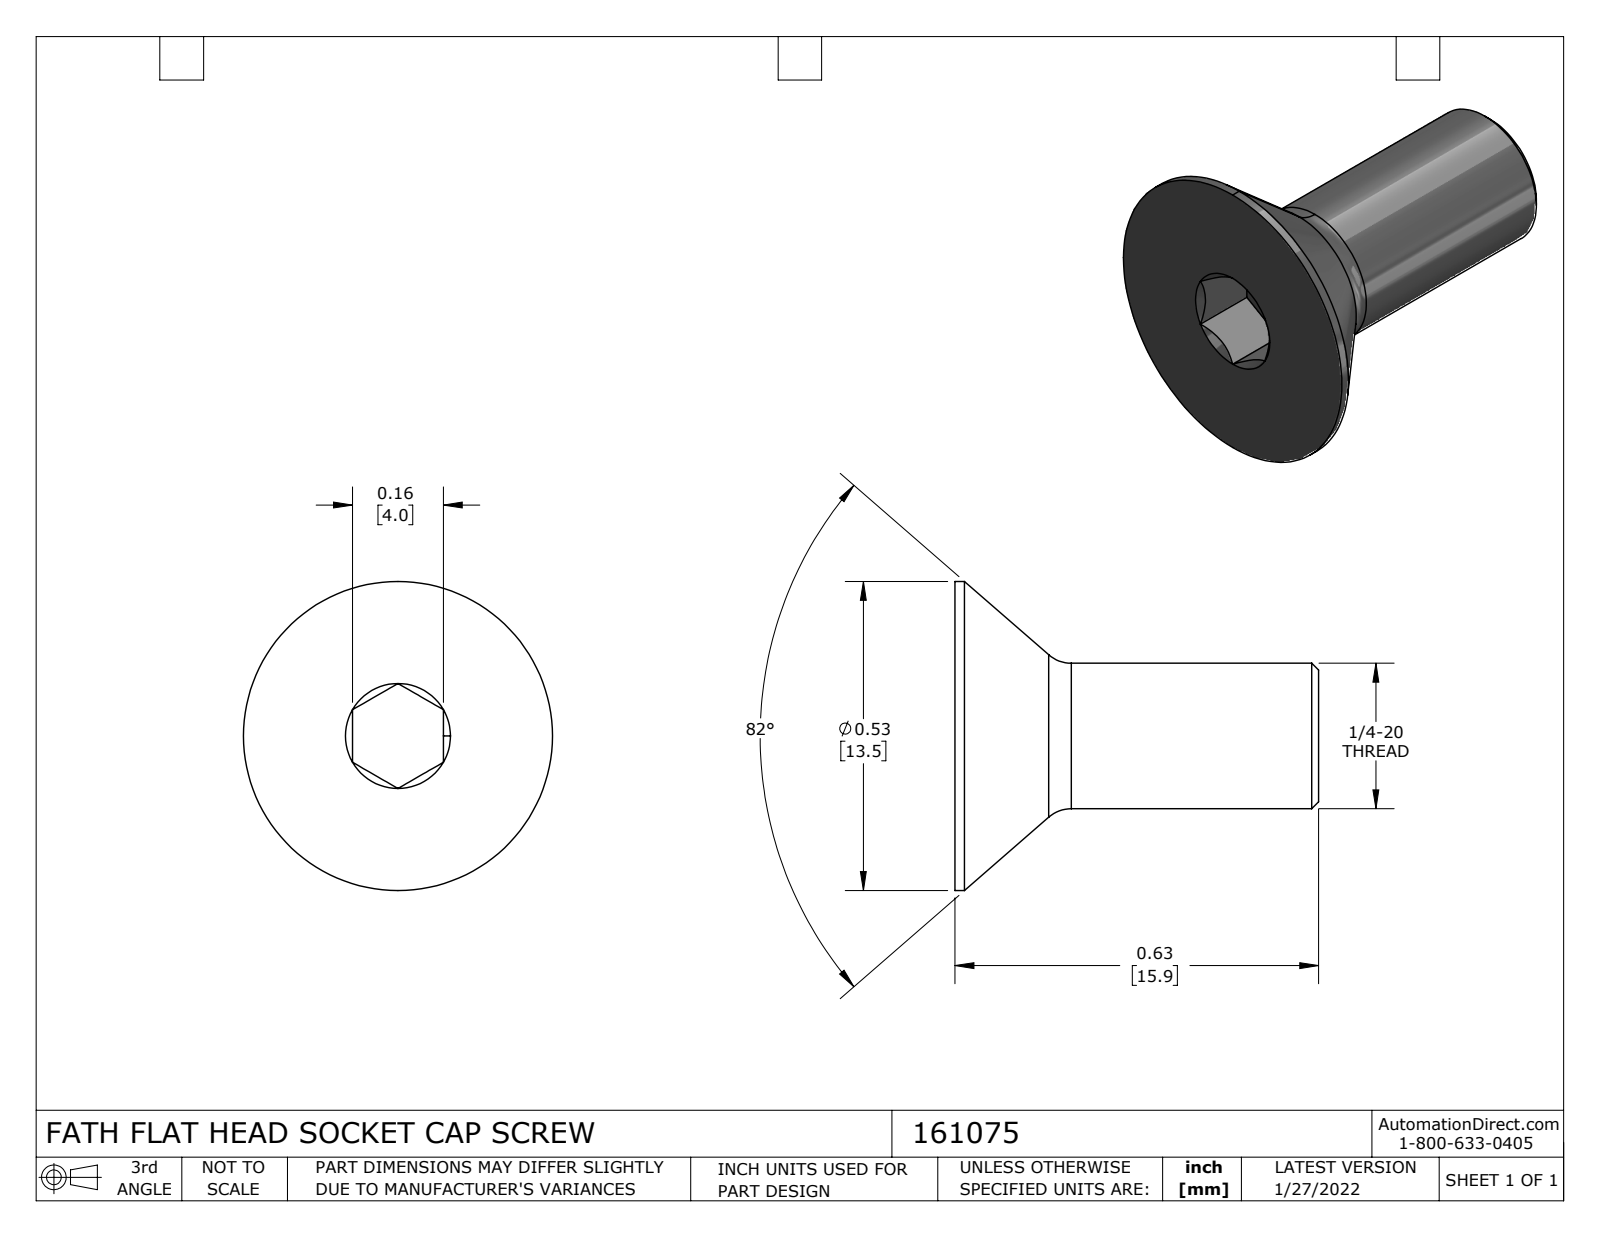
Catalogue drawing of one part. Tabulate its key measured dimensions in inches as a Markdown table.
| quantity | value |
| --- | --- |
| part name | 161075 |
| STEP written by | SolidWorks 2021 (CONFIG_CONTROL_DESIGN) |
| units | inches |
| bodies | 1 solid, 26 faces (9 planar, 4 cylindrical, 13 other) |
| overall size | 0.625 × 0.531 × 0.531 |
| volume | 0.043 in³ |
| surface area | 0.963 in² |
| round bosses / shafts (diameter × count) | 0.531 × 1, 0.25 × 1 |
| main face-to-face distances | 0.625, 0.156, 0.513, 0.113 |
